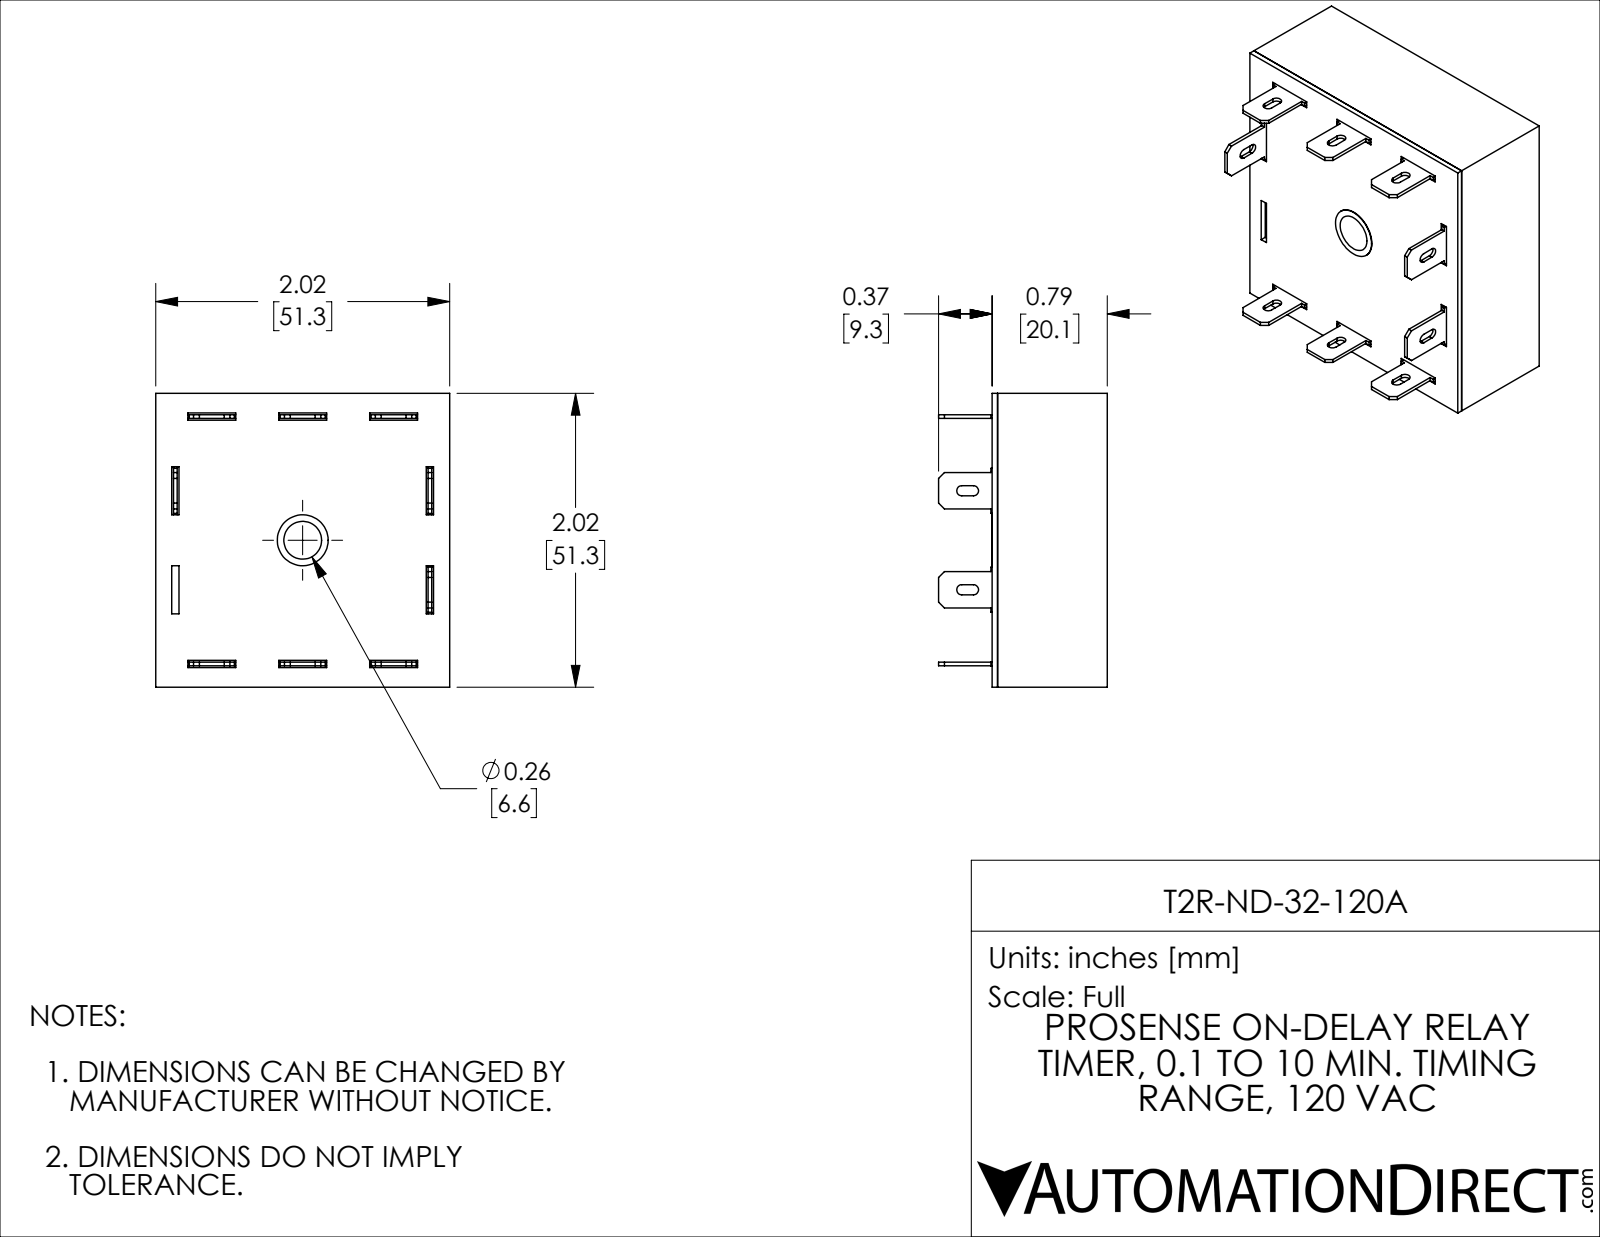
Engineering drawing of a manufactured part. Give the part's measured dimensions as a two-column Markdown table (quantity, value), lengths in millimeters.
| quantity | value |
| --- | --- |
| part name | T2R-ND-32-120A |
| STEP written by | SolidWorks 2021 (CONFIG_CONTROL_DESIGN) |
| units | millimeters |
| bodies | 11 solids, 280 faces (256 planar, 22 cylindrical, 2 other) |
| overall size | 51.31 × 51.31 × 29.46 |
| volume | 11 178 mm³ |
| surface area | 23 301 mm² |
| round holes (diameter × count) | 8.89 × 1 |
| partial cylindrical surfaces (radius × count) | 0.89 × 10 |
| main face-to-face distances | 1.14, 50.16, 19.15, 20.12, 0.97, 18.01, 18.98, 51.3, 3.74, 47.56 |
